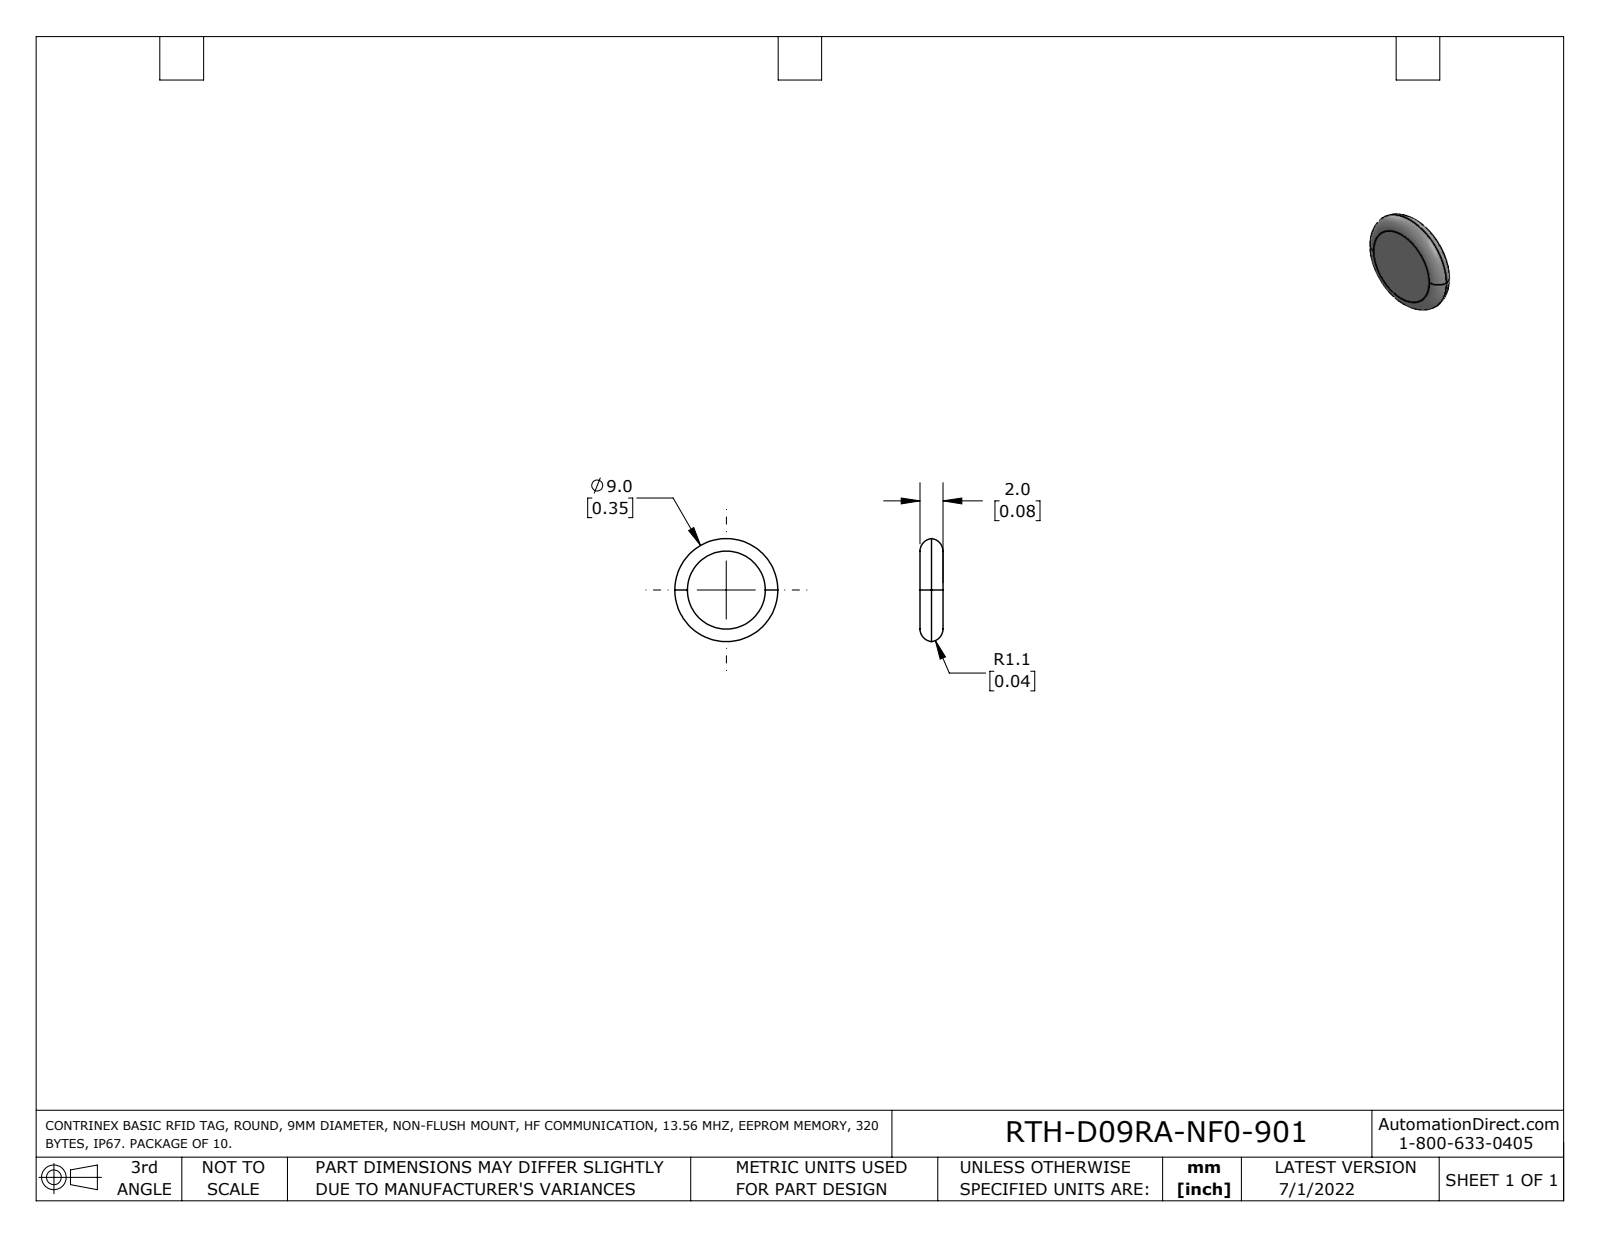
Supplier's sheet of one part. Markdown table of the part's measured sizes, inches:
| quantity | value |
| --- | --- |
| part name | RTP-0090-020 |
| STEP written by | SolidWorks 2021 (AUTOMOTIVE_DESIGN) |
| units | inches |
| bodies | 1 solid, 6 faces (2 planar, 0 cylindrical, 4 other) |
| overall size | 0.354 × 0.354 × 0.079 |
| volume | 0.007 in³ |
| surface area | 0.242 in² |
| main face-to-face distances | 0.079 |
